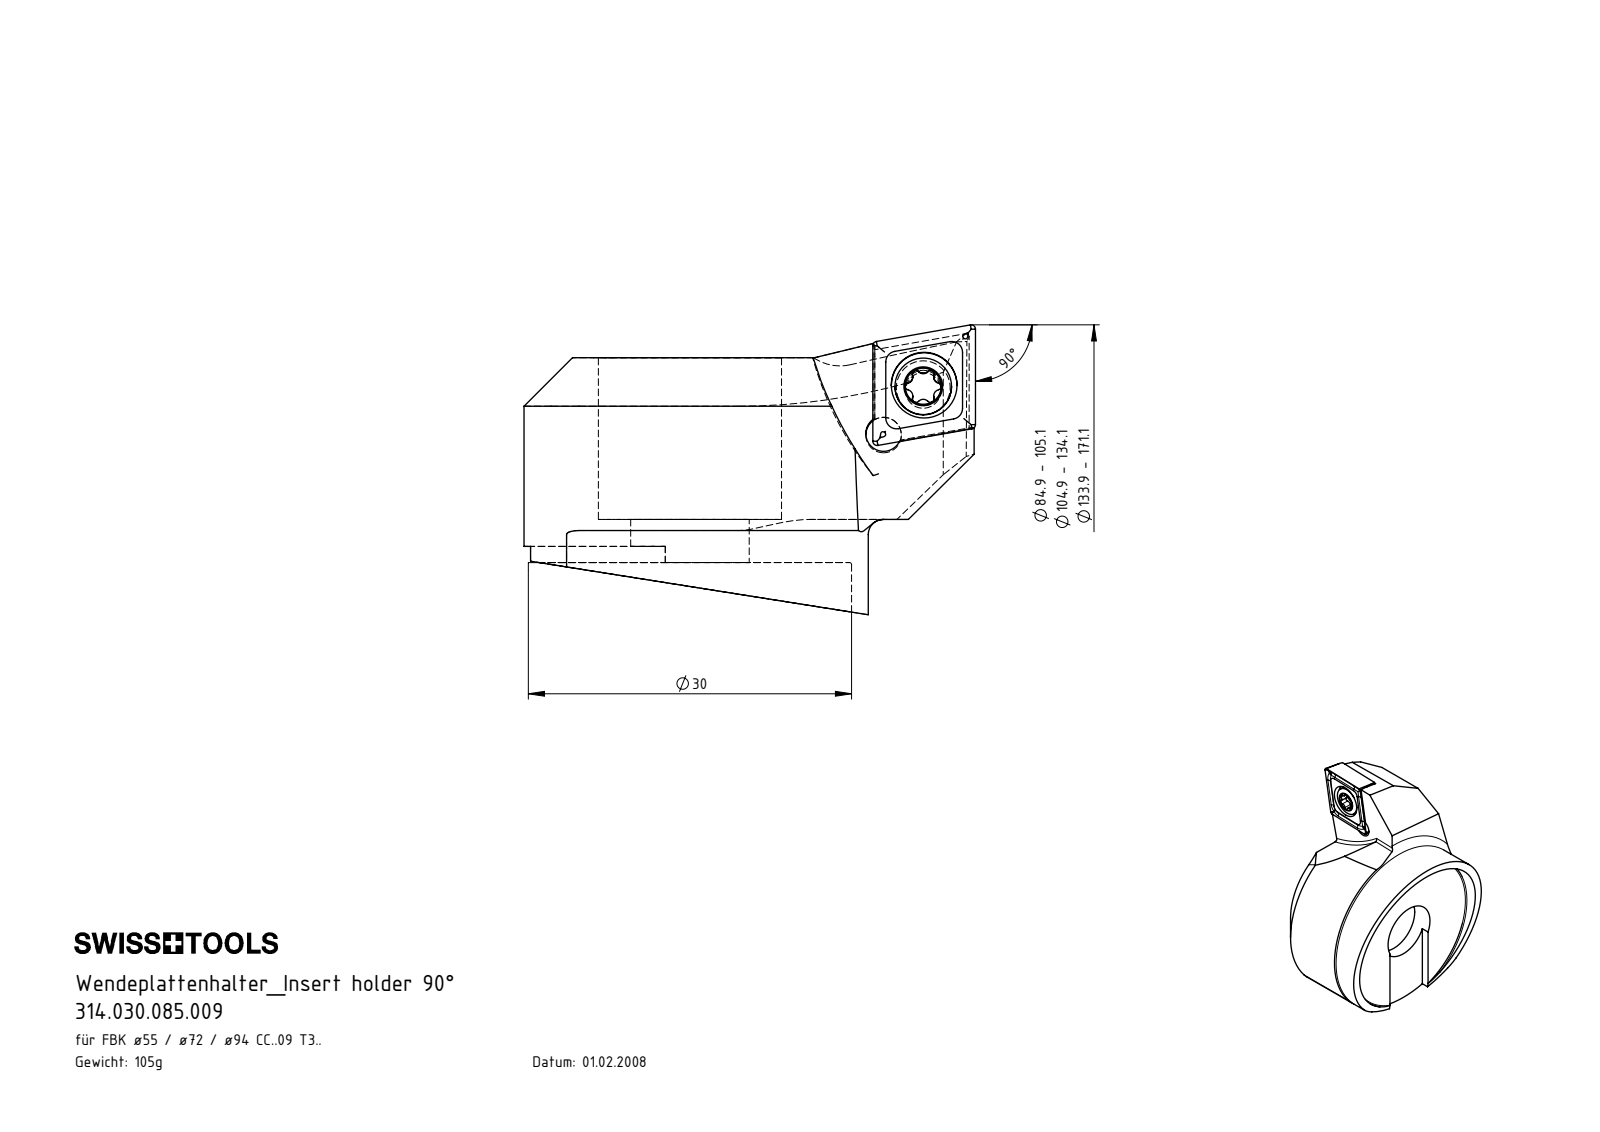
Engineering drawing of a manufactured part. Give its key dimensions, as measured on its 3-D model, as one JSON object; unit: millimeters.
{"part_name": "F55.WCB.001.022; CCMT09T304; WCB-ER2.001.009_A; F55-WCB.001.022_D_fertigbearbeitet", "step_written_by": "SolidWorks 2017 (AUTOMOTIVE_DESIGN)", "units": "millimeters", "bodies": {"solids": 3, "faces": 120, "planar": 41, "cylindrical": 31, "other": 48}, "overall_size": [41.9, 33.2, 26.89], "volume_mm3": 13329, "surface_area_mm2": 5651, "round_holes": [[3.3, 2], [4.4, 1], [6.1, 1], [11, 1], [17, 1], [30, 1]], "round_bosses_or_shafts": [[5.25, 1], [4, 1]], "partial_cylinders_radius": [[0.34, 6], [0.59, 6], [0.5, 2], [10, 2], [5, 1], [16.55, 1], [16.6, 1], [20.9, 1]], "face_to_face_distances": [19, 15, 4, 17.5, 2.5, 1.5, 3.77, 3.97, 10, 9], "hole_center_spacings": [5.73, 5.86]}
